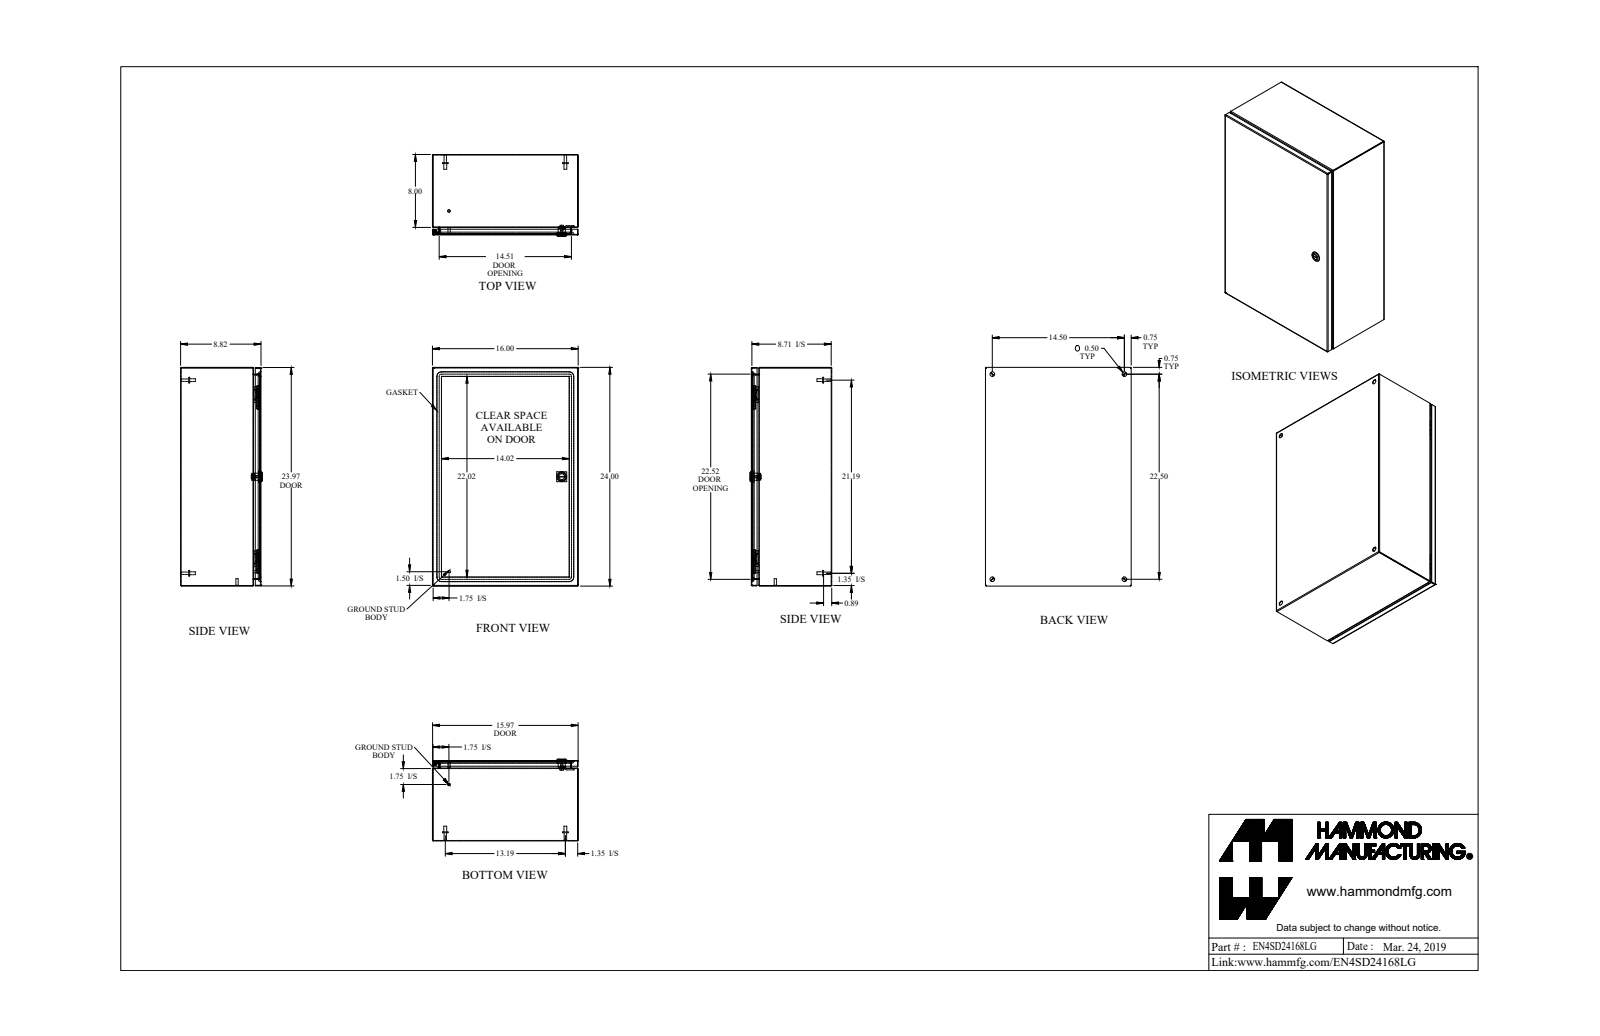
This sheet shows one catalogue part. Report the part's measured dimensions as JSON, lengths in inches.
{"part_name": "EN4SD24168LG_Default", "step_written_by": "SolidWorks 2019 (CONFIG_CONTROL_DESIGN)", "units": "inches", "bodies": {"solids": 21, "faces": 634, "planar": 285, "cylindrical": 213, "other": 136}, "overall_size": [24, 16, 8.982], "volume_in3": 96.99, "surface_area_in2": 3304, "round_holes": [[0.5, 4], [0.172, 1], [0.232, 1], [0.24, 1], [0.242, 1], [0.625, 1], [0.785, 1]], "round_bosses_or_shafts": [[0.625, 4], [0.313, 4], [0.27, 4], [0.281, 2], [0.25, 2], [1.1, 1], [0.525, 1], [0.455, 1]], "partial_cylinders_radius": [[0.029, 21], [0.086, 21], [0.25, 16], [19, 8], [0.006, 4], [0.062, 4], [0.499, 4], [0.125, 2]], "face_to_face_distances": [0.057, 8.765, 8.708, 8.822, 15.943, 23.943, 15.886, 16, 23.886, 24], "hole_center_spacings": [14.5, 22.5, 26.767, 11.299, 11.3, 17.528, 17.528]}
